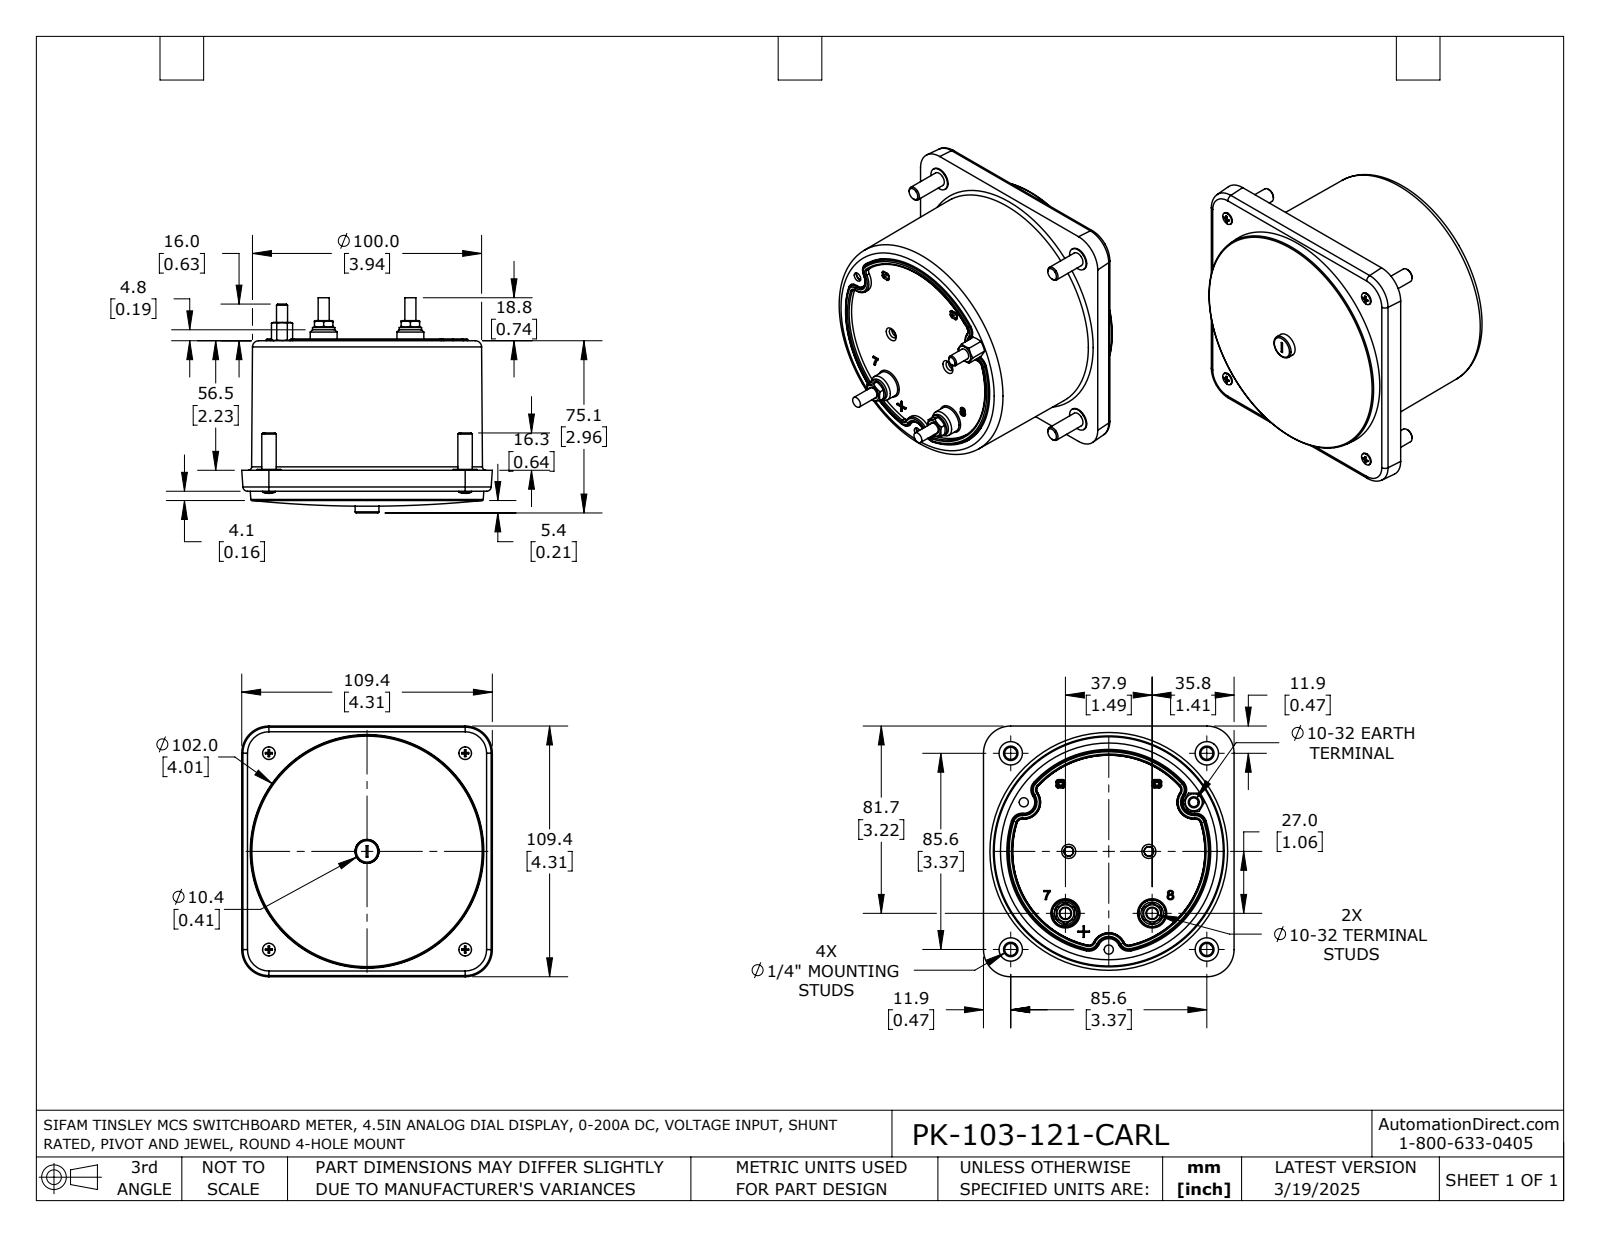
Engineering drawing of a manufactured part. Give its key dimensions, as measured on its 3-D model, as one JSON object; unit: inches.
{"part_name": "PK-103-121-CARL", "step_written_by": "SolidWorks 2021 (AUTOMOTIVE_DESIGN)", "units": "inches", "bodies": {"solids": 1, "faces": 609, "planar": 167, "cylindrical": 141, "other": 301}, "overall_size": [4.307, 4.307, 3.697], "volume_in3": 36.28, "surface_area_in2": 82.21, "round_holes": [[0.094, 4], [0.138, 4], [0.315, 4], [0.157, 3], [0.209, 2]], "round_bosses_or_shafts": [[0.402, 4], [0.248, 4], [0.217, 4], [0.114, 4], [0.19, 3], [0.384, 2], [0.146, 1]], "partial_cylinders_radius": [[0.02, 24], [0.189, 9], [0.079, 4], [1.752, 1]], "face_to_face_distances": [2.177, 2.537, 0.36, 0.048, 2.225, 2.585, 0.489, 2.715, 2.667, 0.129], "hole_center_spacings": [3.372, 3.37, 3.374, 3.378, 3.38, 4.769, 0.971, 1.126]}
